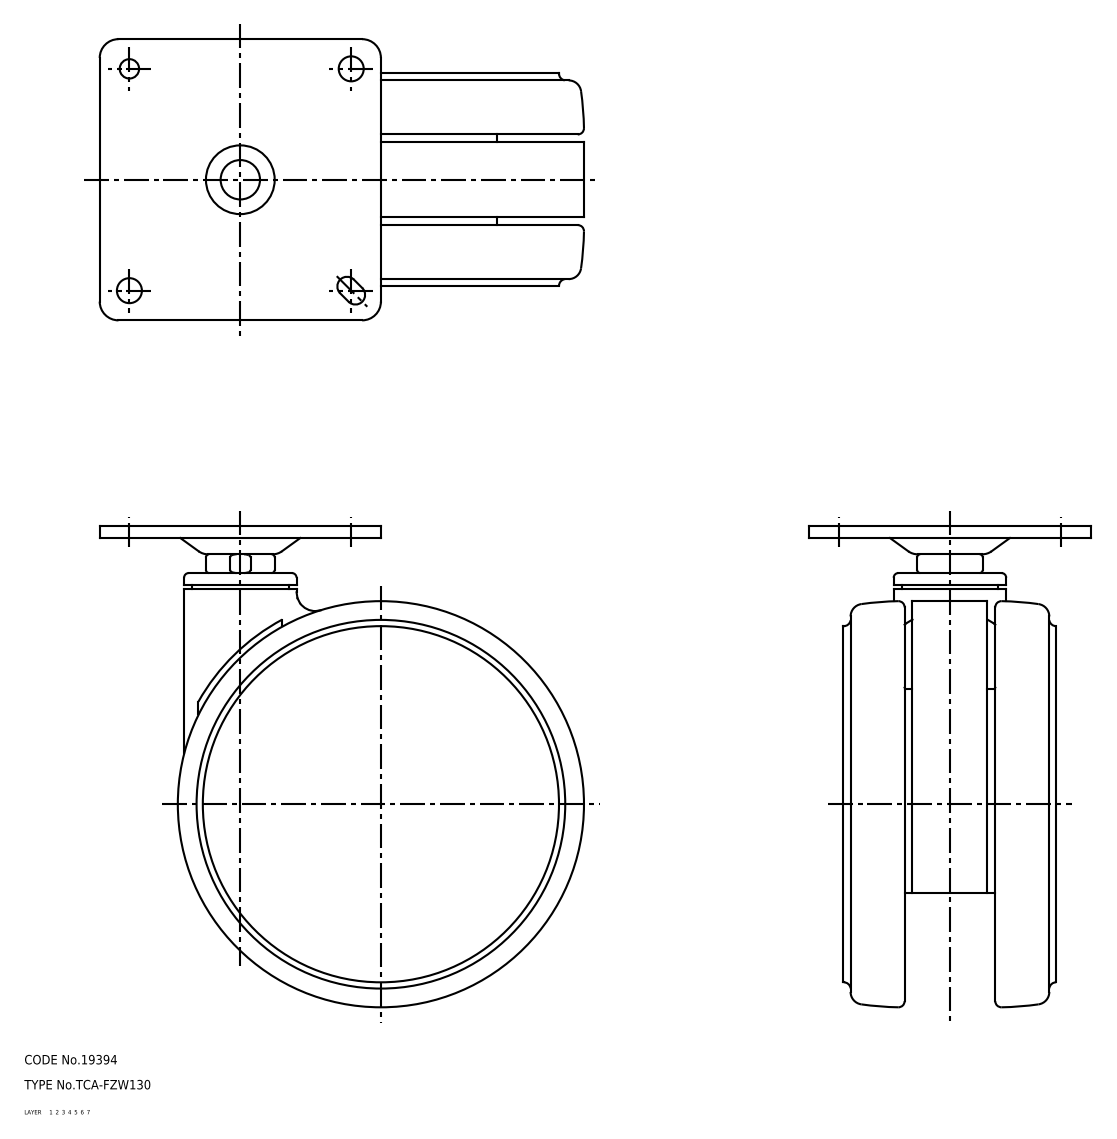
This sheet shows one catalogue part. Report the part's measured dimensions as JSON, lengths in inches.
{"part_name": "caster; TCA-FZW130", "step_written_by": "SolidWorks 2015 (AUTOMOTIVE_DESIGN)", "units": "inches", "bodies": {"solids": 1, "faces": 2312, "planar": 653, "cylindrical": 957, "other": 702}, "overall_size": [6.102, 6.063, 3.543], "volume_in3": 31.43, "surface_area_in2": 317.2, "round_holes": [[0.315, 2], [0.244, 1], [0.394, 1], [0.398, 1], [0.413, 1], [0.472, 1], [0.591, 1], [0.598, 1], [0.622, 1], [0.63, 1], [0.756, 1], [1.024, 1]], "round_bosses_or_shafts": [[4.638, 1], [4.488, 1], [1.654, 1], [1.417, 1], [1.22, 1], [1.098, 1], [1.087, 1], [0.866, 1]], "partial_cylinders_radius": [[0.059, 201], [0.039, 98], [0.02, 78], [0.012, 44], [0.008, 16], [0.118, 16], [0.236, 4], [0.122, 2]], "face_to_face_distances": [0.15, 0.079, 2.606, 0.071, 2.457, 2.535, 0.445, 2.24, 0.366, 2.161], "hole_center_spacings": [1.976, 2.795, 3.953]}
